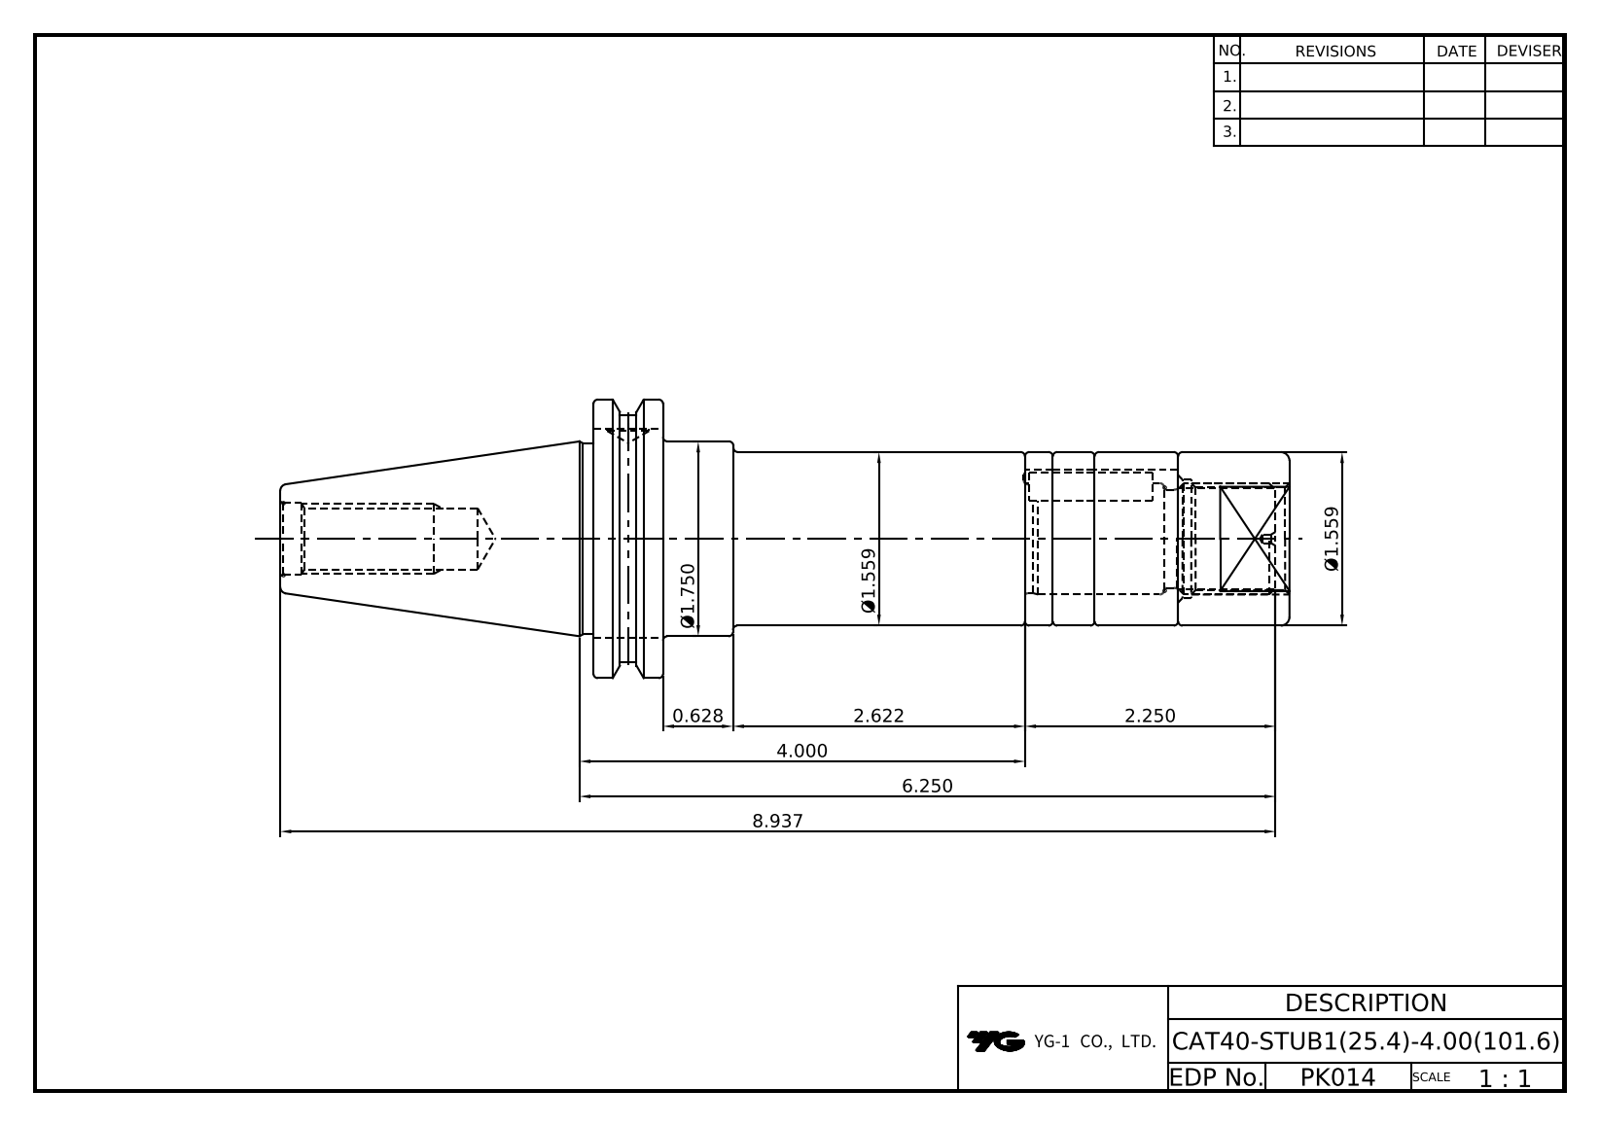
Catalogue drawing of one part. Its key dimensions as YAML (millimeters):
part_name: "LO-CAT40-STUB25.4-101.6; 6.35x6.35x28; COLLAR_STUB25.4(6.35T); COLLAR_STUB25.4(9.525T) (+2 more)"
step_written_by: "Autodesk Inventor 2025 (AP242_MANAGED_MODEL_BASED_3D_ENGINEERING_MIM_LF)"
units: millimeters
bodies: {solids: 6, faces: 113, planar: 59, cylindrical: 28, other: 26}
overall_size: [228.82, 63.5, 61.09]
volume: 283790
surface_area: 52154
round_holes:
  - {diameter: 9.53, count: 1}
  - {diameter: 13.39, count: 1}
  - {diameter: 16.3, count: 1}
  - {diameter: 23.11, count: 1}
  - {diameter: 25.7, count: 1}
  - {diameter: 27, count: 1}
round_bosses_or_shafts:
  - {diameter: 63.5, count: 1}
  - {diameter: 56.3, count: 1}
  - {diameter: 44.45, count: 1}
  - {diameter: 43.6, count: 1}
  - {diameter: 39.6, count: 1}
  - {diameter: 25.4, count: 1}
  - {diameter: 22.4, count: 1}
partial_cylinders:
  - {radius: 3.17, count: 3}
face_to_face_distances: [82.55, 15.88, 98.43, 103.43, 112.95, 87.55, 97.07, 5, 14.52, 9.52]
